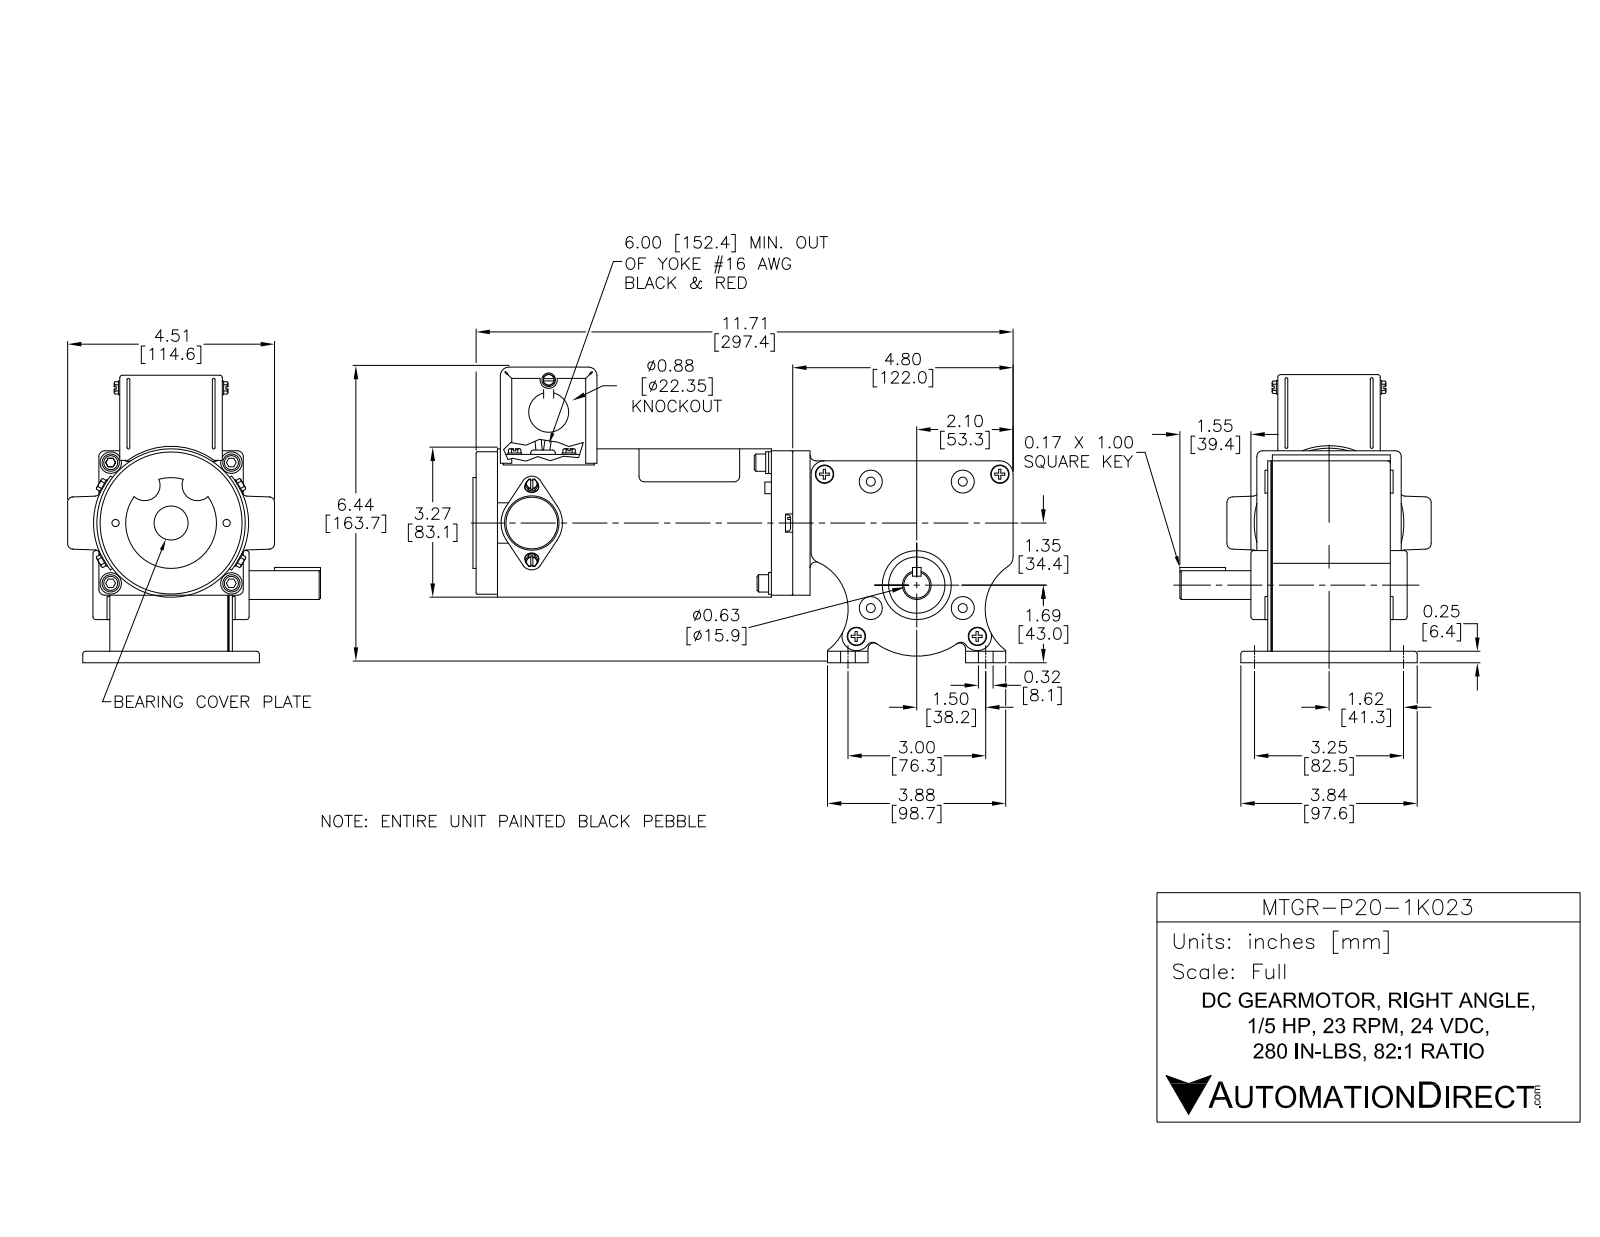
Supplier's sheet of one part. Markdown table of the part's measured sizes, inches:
| quantity | value |
| --- | --- |
| part name | P20-1K022 |
| STEP written by | SolidWorks 2013 (AUTOMOTIVE_DESIGN) |
| units | inches |
| bodies | 43 solids, 797 faces (486 planar, 283 cylindrical, 28 other) |
| overall size | 11.791 × 6.522 × 5.415 |
| volume | 64.64 in³ |
| surface area | 475.7 in² |
| round holes (diameter × count) | 0.5 × 5, 0.125 × 4, 0.197 × 4, 0.4 × 4, 0.198 × 2, 0.25 × 1, 0.3 × 1, 0.375 × 1, 0.625 × 1, 1 × 1, 1.125 × 1, 1.5 × 1 |
| round bosses / shafts (diameter × count) | 0.375 × 6, 0.3 × 4, 0.375 × 3, 0.125 × 2, 0.1 × 2, 3.156 × 1, 0.625 × 1, 0.301 × 1 |
| partial cylindrical surfaces (radius × count) | 0.125 × 4, 0.16 × 4, 0.191 × 4, 0.234 × 4, 0.25 × 4, 0.13 × 2, 0.159 × 2, 0.29 × 2 |
| main face-to-face distances | 0.015, 0.03, 0.031, 2.603, 2.588, 2.573, 0.1, 0.07, 0.085, 2.673 |
| hole center spacings | 1.318, 1.859, 2.63, 2.865, 1.118, 1.23, 2, 2.37 |
